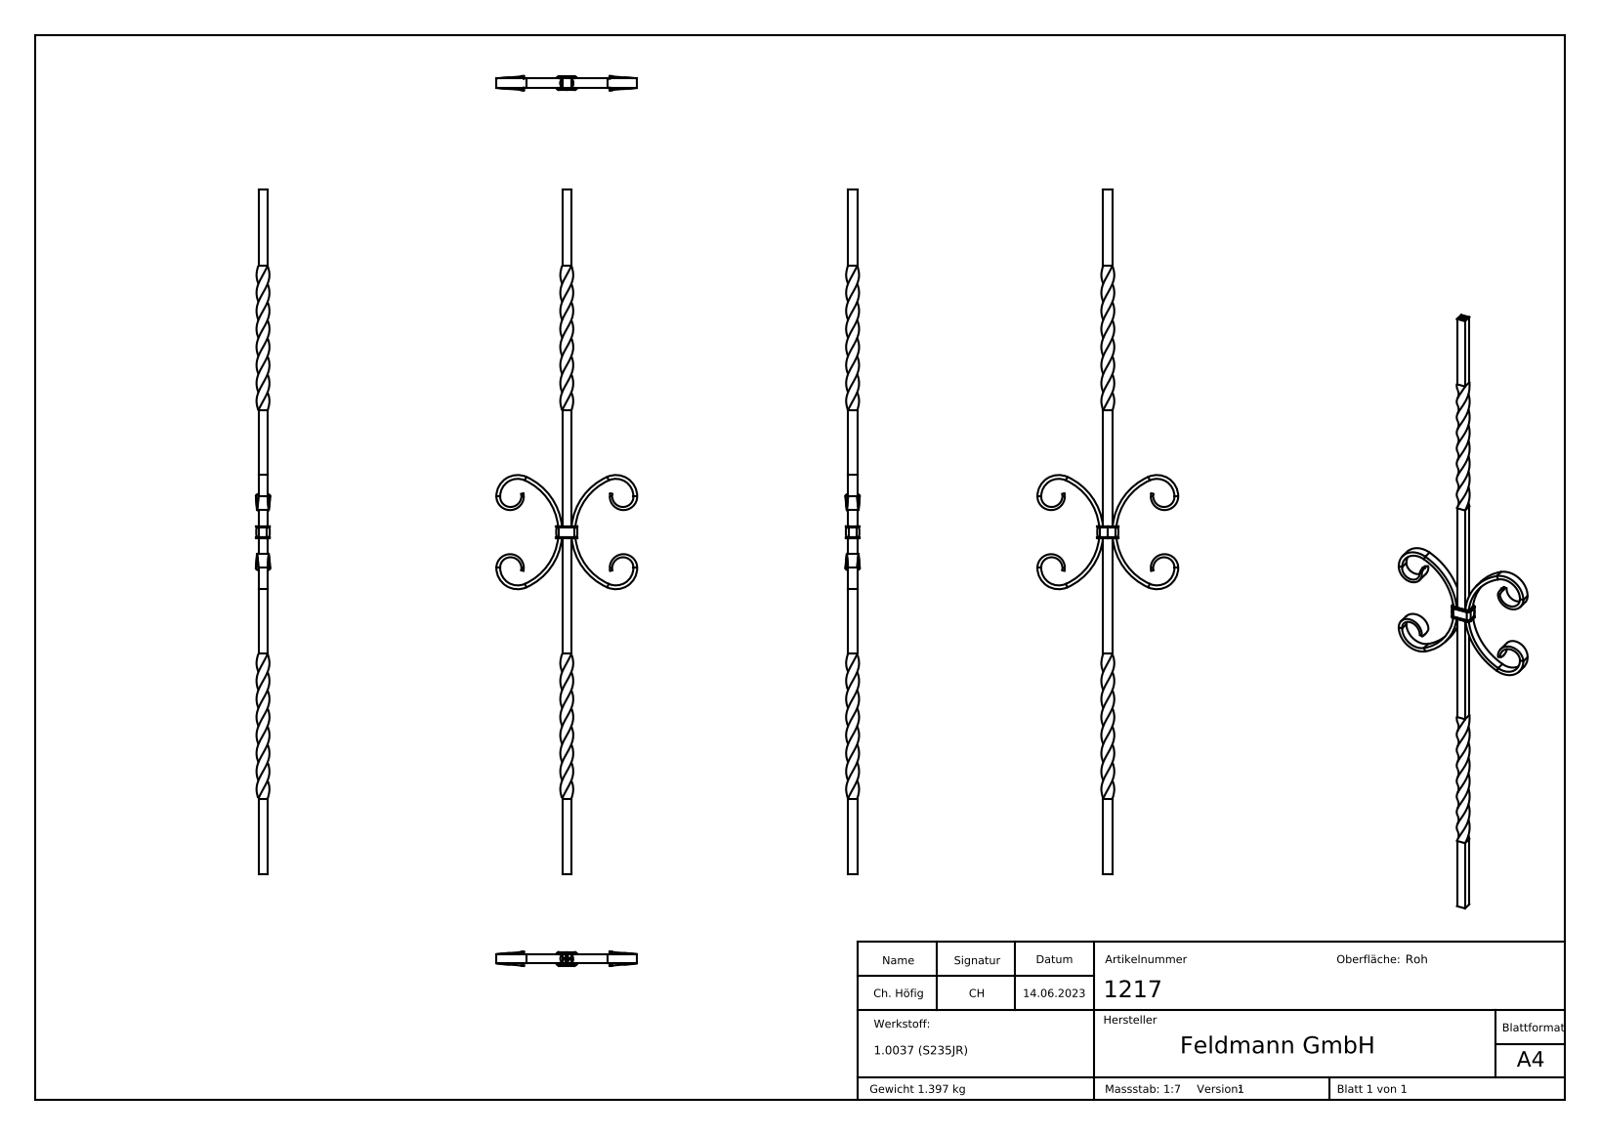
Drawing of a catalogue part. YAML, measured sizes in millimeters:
part_name: "1217"
step_written_by: "SolidWorks 2018 (CONFIG_CONTROL_DESIGN)"
units: millimeters
bodies: {solids: 4, faces: 408, planar: 197, cylindrical: 69, other: 142}
overall_size: [900, 185, 18.6]
volume: 179118
surface_area: 74273
partial_cylinders:
  - {radius: 0.5, count: 24}
  - {radius: 0.2, count: 8}
  - {radius: 1, count: 4}
  - {radius: 4, count: 4}
  - {radius: 21.62, count: 4}
  - {radius: 23, count: 4}
  - {radius: 28, count: 4}
  - {radius: 74.46, count: 2}
face_to_face_distances: [12, 5, 17, 442, 458, 16, 22, 900, 3, 15]
